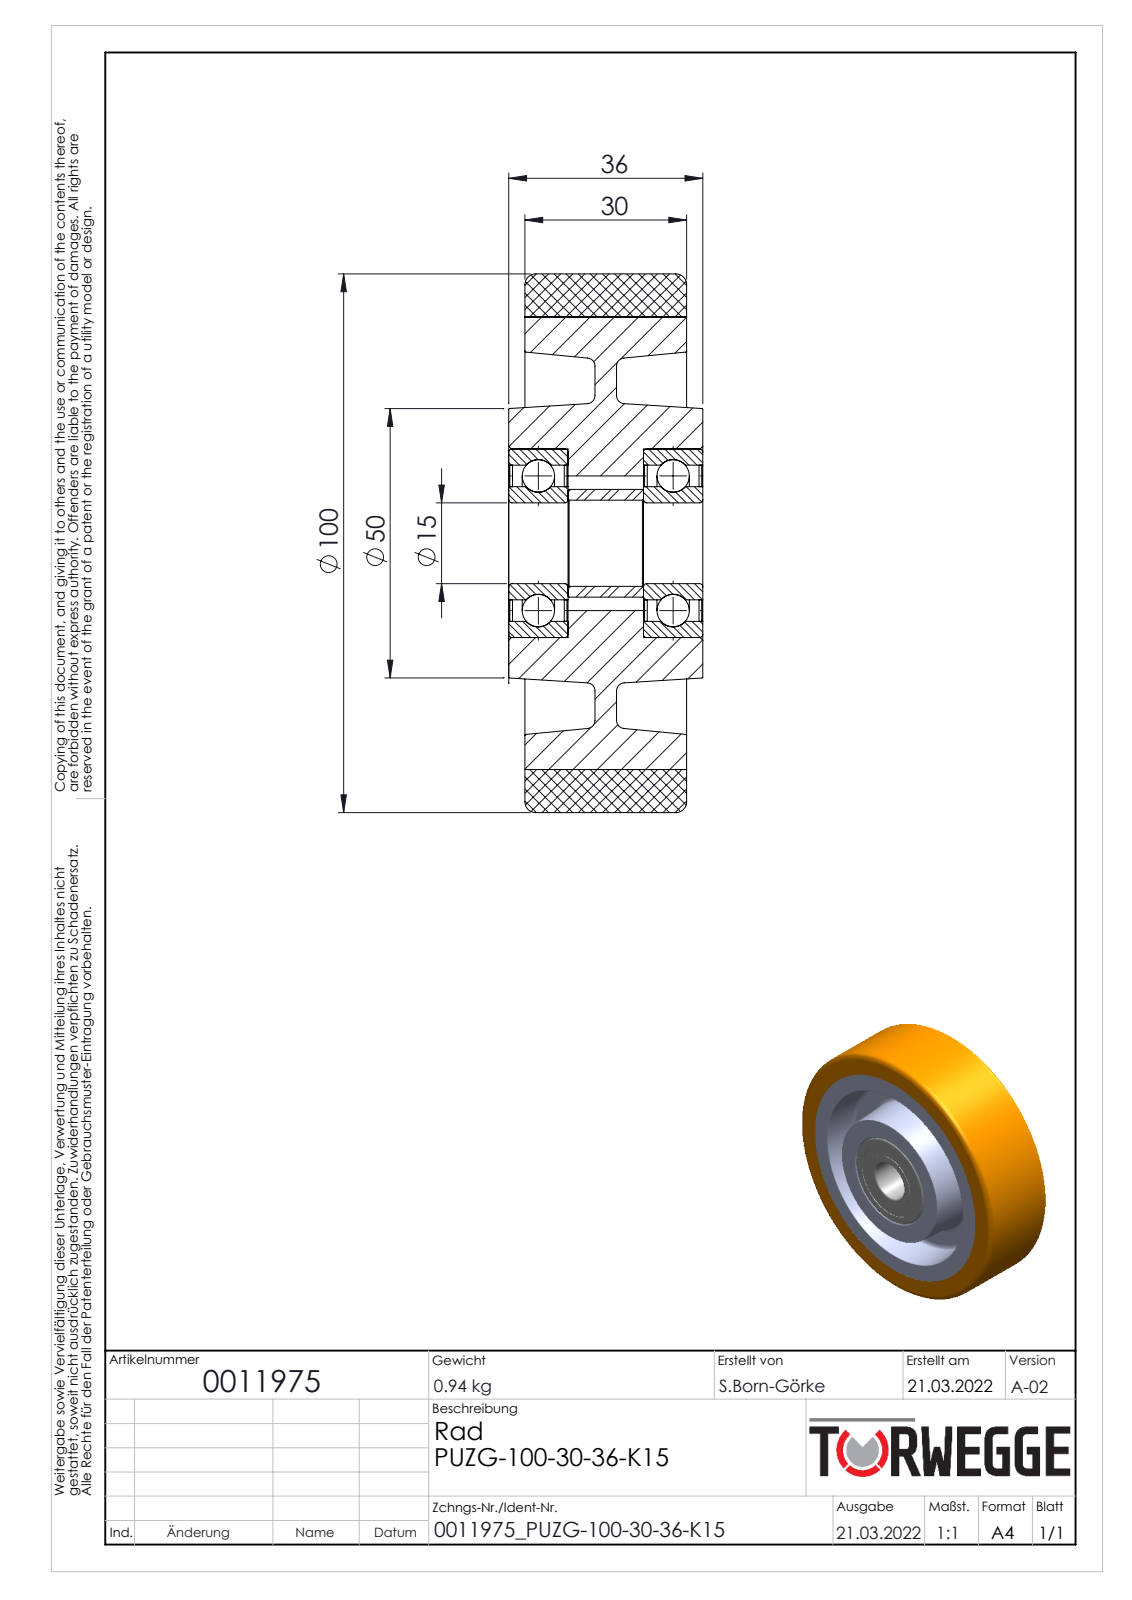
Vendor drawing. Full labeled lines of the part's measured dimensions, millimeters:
Part name (STEP PRODUCT): 0011975
STEP written by: SolidWorks 2020 (AUTOMOTIVE_DESIGN)
Units: millimetres
Bodies: 13 solids, 160 faces (28 planar, 56 cylindrical, 76 other)
Overall size (bounding box): 100 × 100 × 36
Volume: 189 251 mm³ · Surface area: 68 837 mm²
Round holes (diameter × count): ⌀15 ×1, ⌀16 ×1, ⌀21 ×1, ⌀25 ×1, ⌀29 ×1, ⌀35 ×1, ⌀84 ×1
Round bosses / shafts (diameter × count): ⌀100 ×1, ⌀20 ×1
Main face-to-face distances: 30, 25, 3, 33, 16, 20, 13, 17, 11, 8
